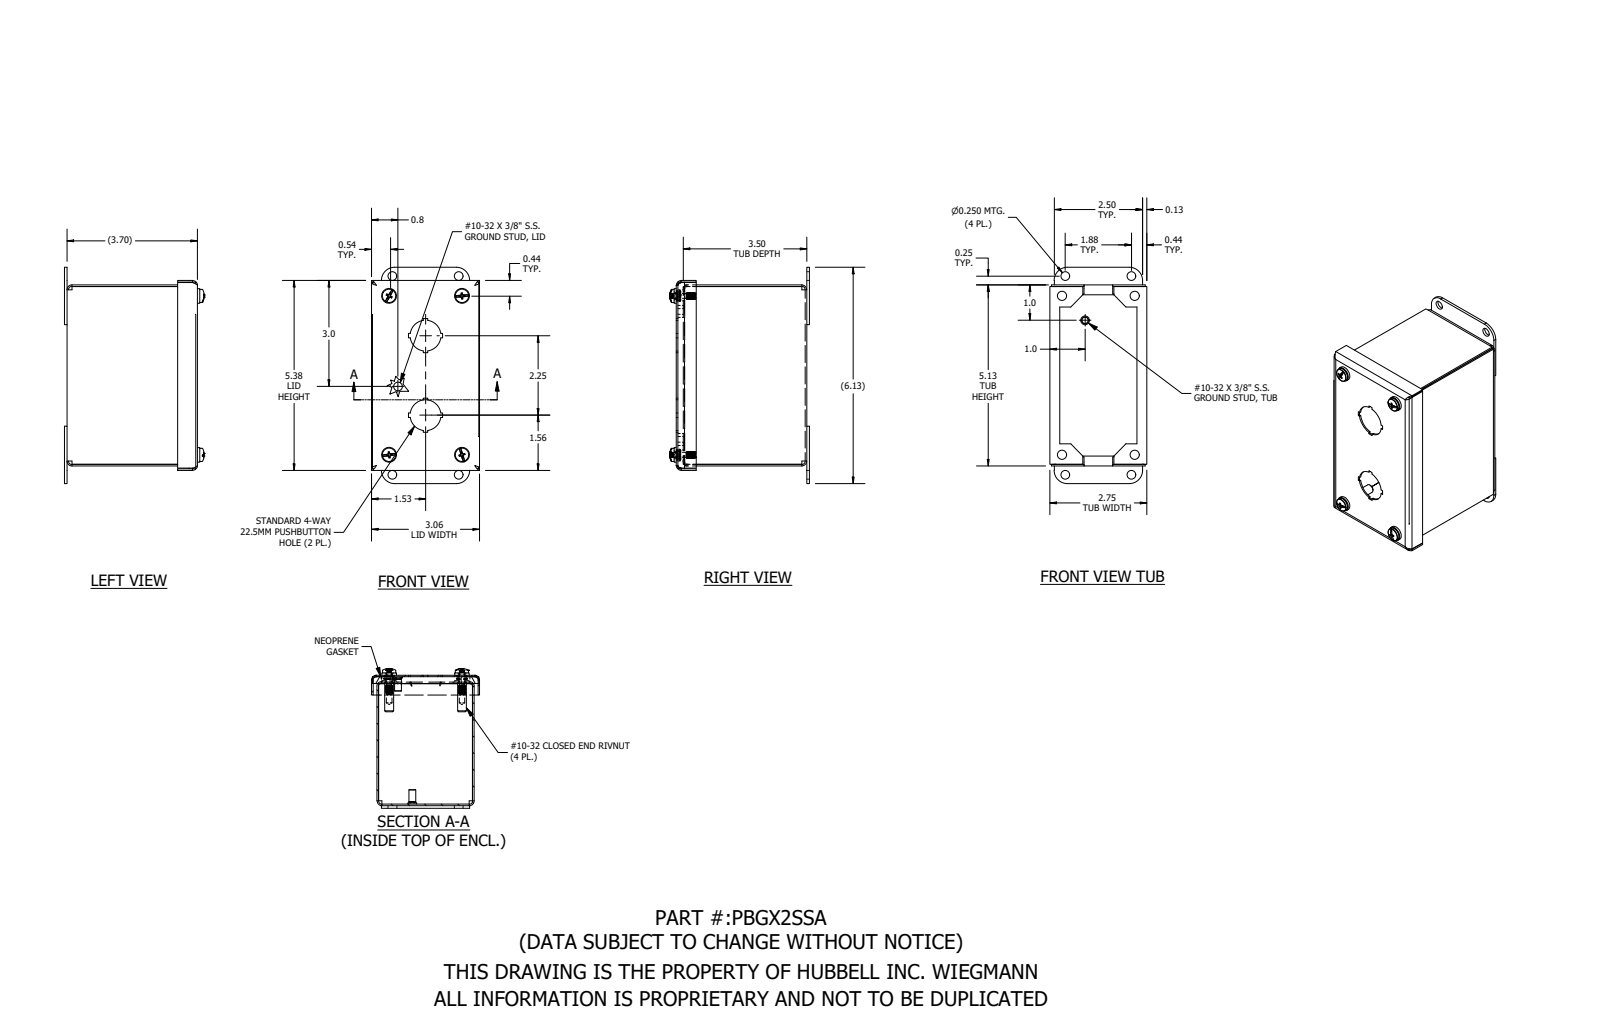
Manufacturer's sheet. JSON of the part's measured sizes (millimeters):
{"part_name": "PBGX2SSA", "step_written_by": "SolidWorks 2021 (AUTOMOTIVE_DESIGN)", "units": "millimeters", "bodies": {"solids": 20, "faces": 744, "planar": 340, "cylindrical": 252, "other": 152}, "overall_size": [155.6, 100.4, 77.8], "volume_mm3": 106800, "surface_area_mm2": 154400, "round_holes": [[4, 4], [5, 4], [6.4, 4], [6.5, 4], [7.1, 4], [8, 4], [3.4, 2], [4.4, 2], [4.4, 2], [22.2, 2]], "round_bosses_or_shafts": [[10.3, 4], [8.1, 4], [6.3, 4], [4.7, 4], [3.6, 4], [3.6, 4], [9.5, 3], [6.4, 2]], "partial_cylinders_radius": [[2.4, 8], [3.5, 8], [1.6, 4], [9.5, 4], [2.7, 3], [2.7, 1]], "face_to_face_distances": [1.1, 1.1, 92.7, 68.7, 69.9, 67.6, 68.7, 93.9, 91.6, 127.9], "hole_center_spacings": [128.6, 90.6, 102.8, 1.5, 14.4, 14.5, 14.5, 38.8]}
